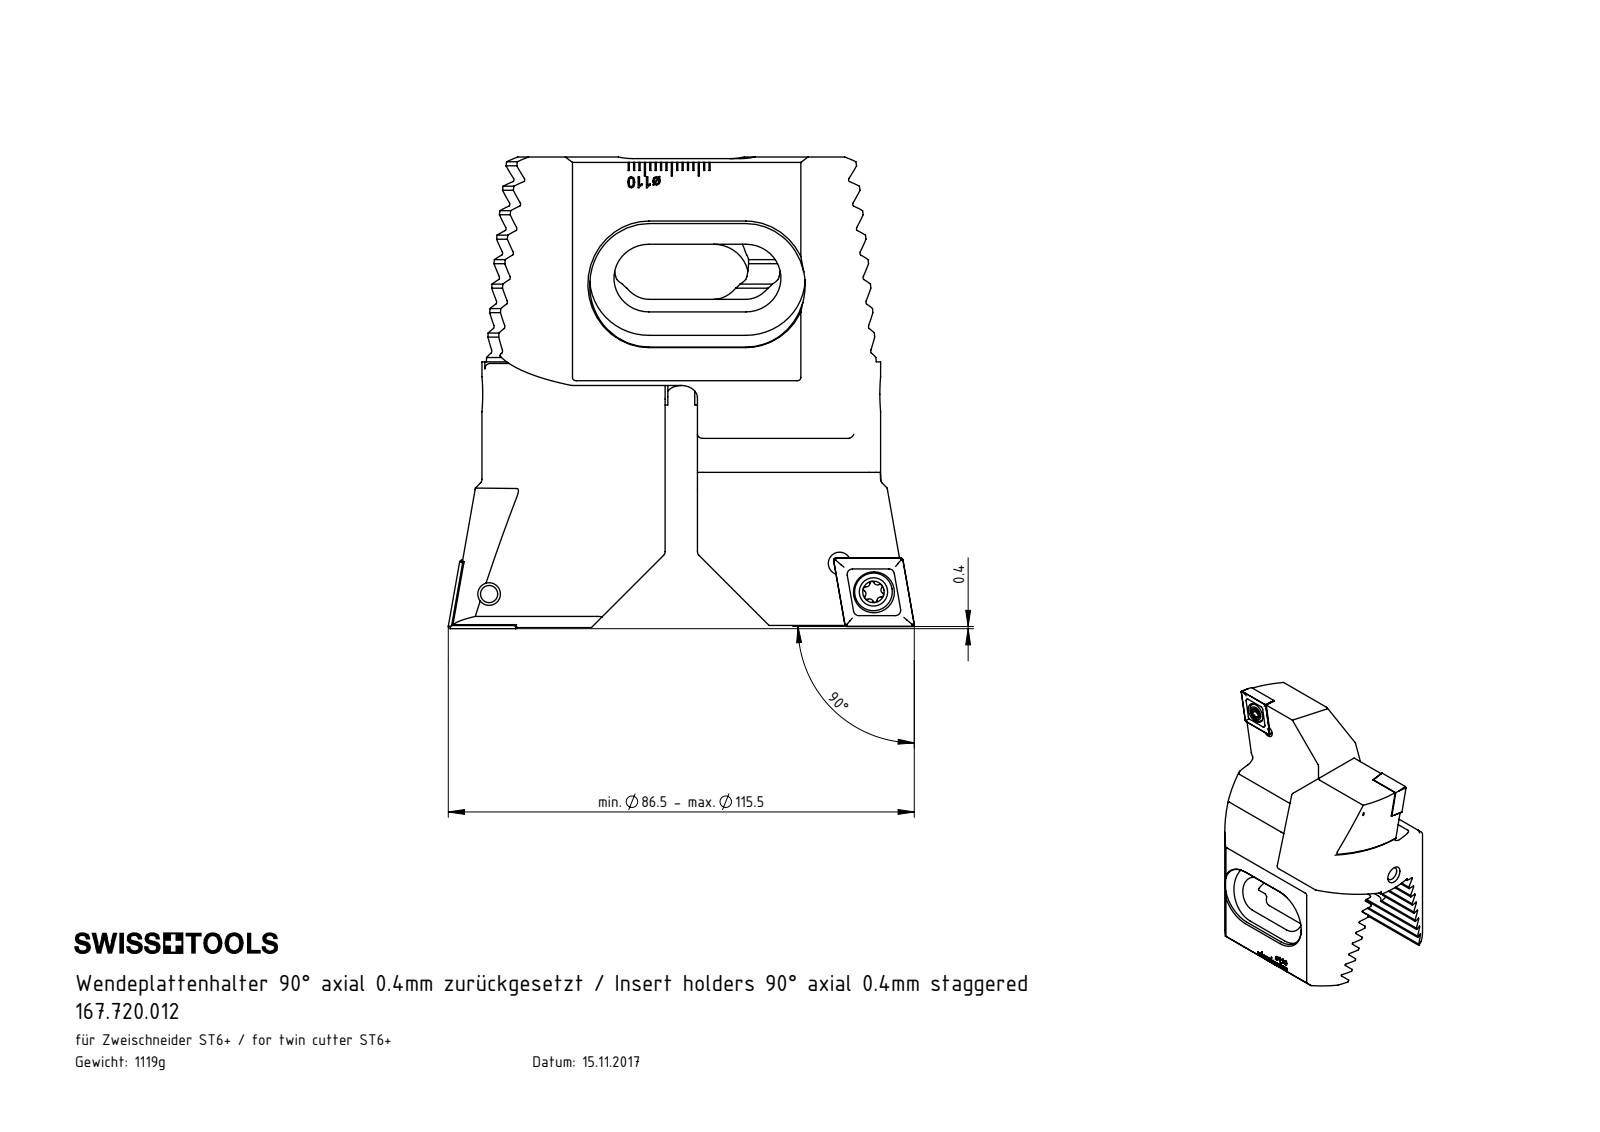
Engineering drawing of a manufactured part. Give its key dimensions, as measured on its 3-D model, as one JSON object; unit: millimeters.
{"part_name": "WCC-ER2.001.010_A; Z72-ER3.001.030; ISO 4028 - M3 x 5_M3x8; ZC7-xxx.001.050_A (+3 more)", "step_written_by": "SolidWorks 2017 (CONFIG_CONTROL_DESIGN)", "units": "millimeters", "bodies": {"solids": 8, "faces": 746, "planar": 411, "cylindrical": 143, "other": 192}, "overall_size": [87.5, 86.5, 58.2], "volume_mm3": 142276, "surface_area_mm2": 37228, "round_holes": [[4.2, 4], [5, 2], [5.5, 2], [7.6, 2], [2, 1], [2.5, 1], [8, 1]], "round_bosses_or_shafts": [[7, 2], [5, 2], [6, 1], [4, 1], [3, 1], [2, 1]], "partial_cylinders_radius": [[0.34, 16], [1, 16], [0.39, 12], [0.69, 6], [0.69, 6], [3, 4], [6.5, 4], [11, 4]], "face_to_face_distances": [4.07, 8.14, 20.36, 12.21, 28.8, 29.4, 58.2, 16.29, 20.34, 24.43], "hole_center_spacings": [8.21, 8.33, 71.43, 20, 58.76, 65.23, 65.3, 65.33]}
